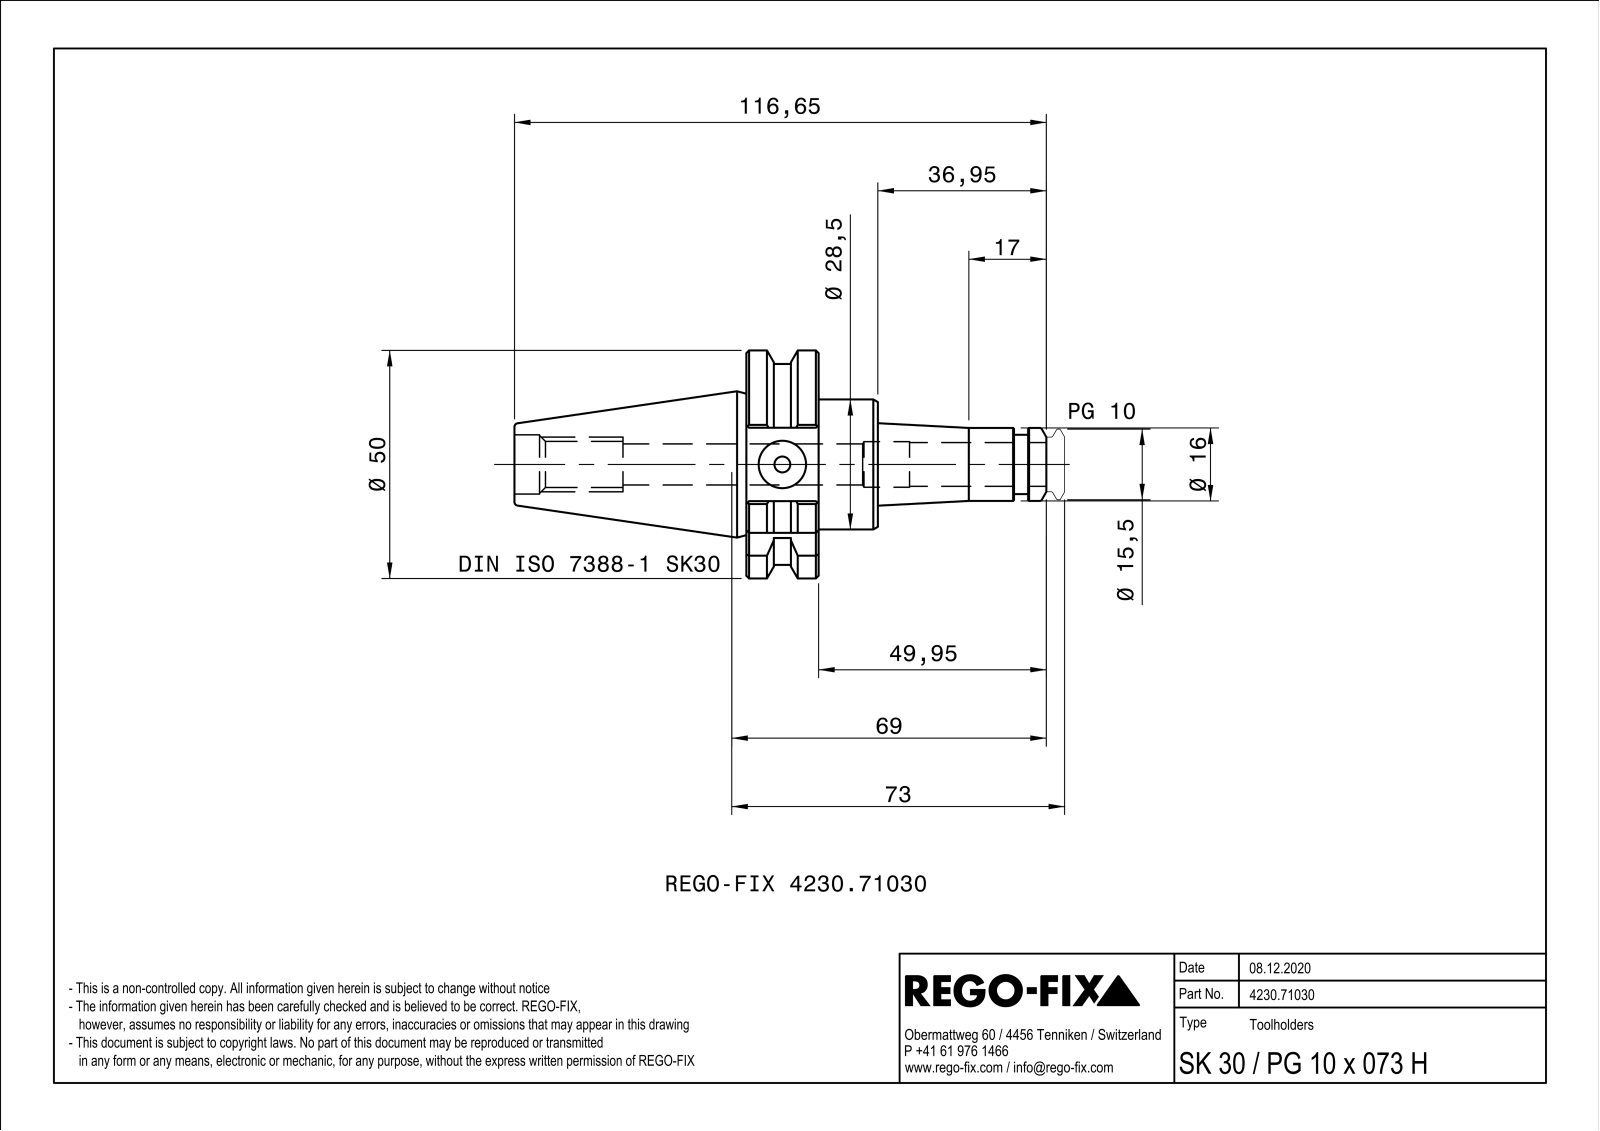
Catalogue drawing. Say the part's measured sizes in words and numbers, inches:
The part is named "NOCUT". Its 3-D file was written by "SIEMENS PLM Software Solid Edge ST10 (AUTOMOTIVE_DESIGN)". It is 1 solid with 138 faces: 44 planar, 41 cylindrical and 53 other. Overall it measures 4.593 by 1.969 by 1.846 inches. Its volume is 3.543 cubic inches and its surface area 26.04 square inches. Round holes: 3 of diameter 0.138, 2 of diameter 0.394, 1 of diameter 0.236, 1 of diameter 0.354, 1 of diameter 0.398, 1 of diameter 0.512. Round bosses or shafts: 1 of diameter 1.122, 1 of diameter 0.63. Partial cylindrical surfaces (rounded edges, fillets, slot ends): 13 of radius 0.02, 1 of radius 0.867, 1 of radius 0.984. The main face-to-face distances are 0.624, 0.512, 1.136, 1.378, 0.634, 0.274, 0.122, 1.297, 1.809, 2.433.
